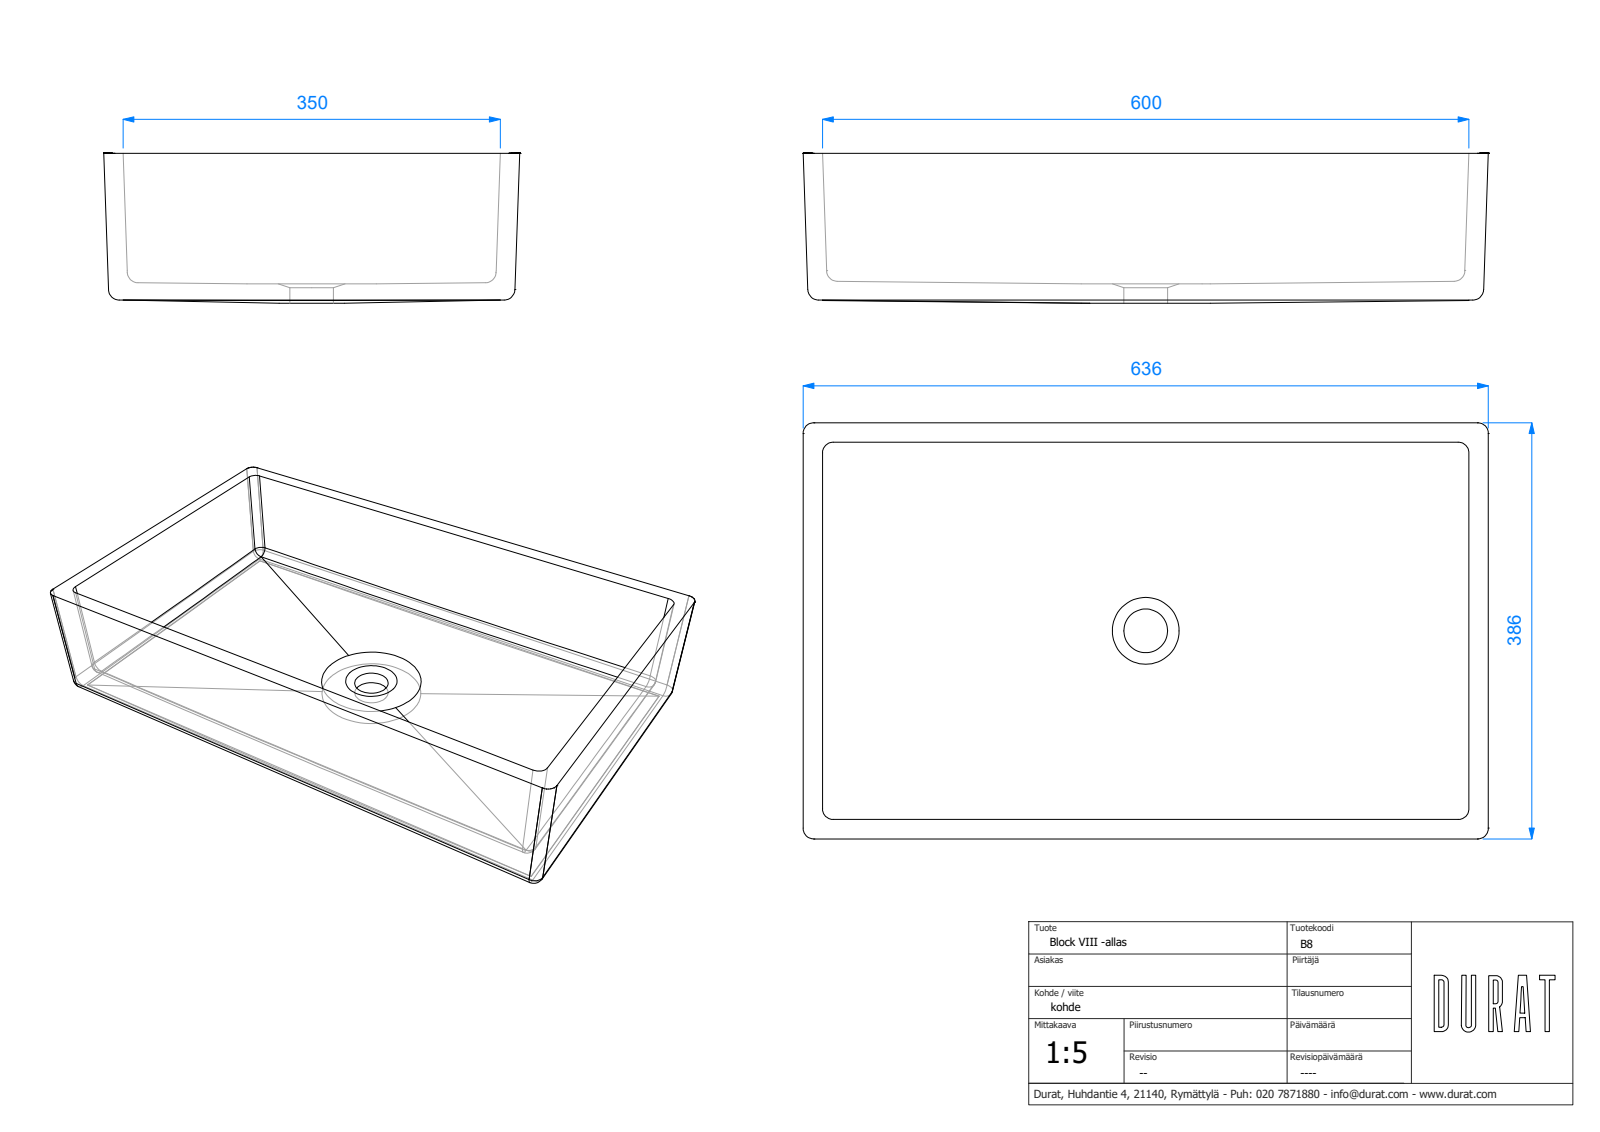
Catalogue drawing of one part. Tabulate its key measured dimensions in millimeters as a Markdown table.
| quantity | value |
| --- | --- |
| STEP written by | ST-DEVELOPER v15 (AUTOMOTIVE_DESIGN) |
| units | millimeters |
| bodies | 0 solids, 48 faces (16 planar, 0 cylindrical, 32 other) |
| overall size | 636.02 × 386.02 × 139.06 |
| main face-to-face distances | 18.01, 17.98, 17.97, 139.06, 18, 121.06, 3.06, 14.94, 136, 350 |
